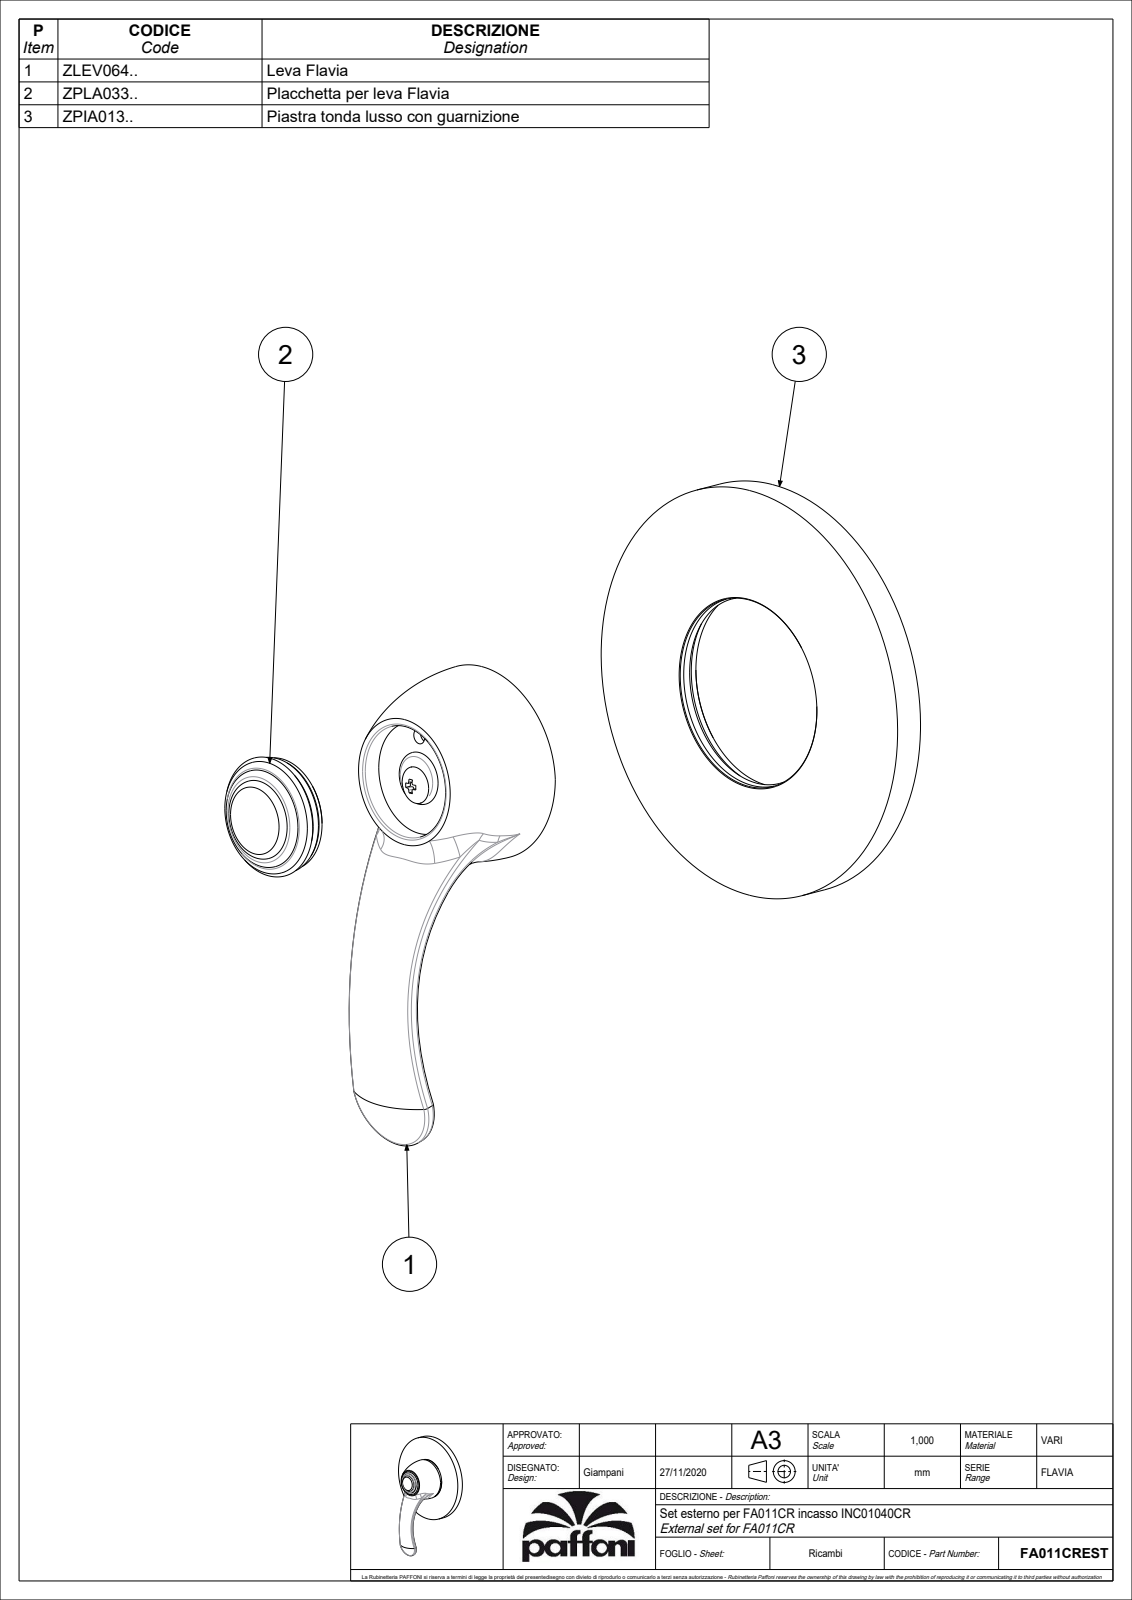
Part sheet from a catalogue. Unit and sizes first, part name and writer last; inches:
Units: inches
Overall size (bounding box): 6.035 × 4.331 × 2.128
Round holes (diameter × count): ⌀0.157 ×1, ⌀0.276 ×1, ⌀1.181 ×1, ⌀1.996 ×1, ⌀2.075 ×1, ⌀2.228 ×1, ⌀4.134 ×1
Round bosses / shafts (diameter × count): ⌀4.331 ×1, ⌀2.35 ×1, ⌀1.177 ×1, ⌀1.063 ×1, ⌀0.386 ×1, ⌀0.157 ×1
Partial cylindrical surfaces — rounded edges, fillets, slot ends (radius × count): R0.02 ×4, R0.059 ×4
Main face-to-face distances: 0.098, 1.044, 0.276, 1.32, 0.217, 1.359, 0.059, 1.418, 1.143, 1.261
Hole centre spacings: 0.064, 0.448, 0.512
Volume: 3.42 in³ · Surface area: 68.91 in²
Bodies: 3 solids, 237 faces (132 planar, 36 cylindrical, 69 other)
Part name (STEP PRODUCT): FA011CREST
STEP written by: CREO PARAMETRIC BY PTC INC, 2020044 (CONFIG_CONTROL_DESIGN)
